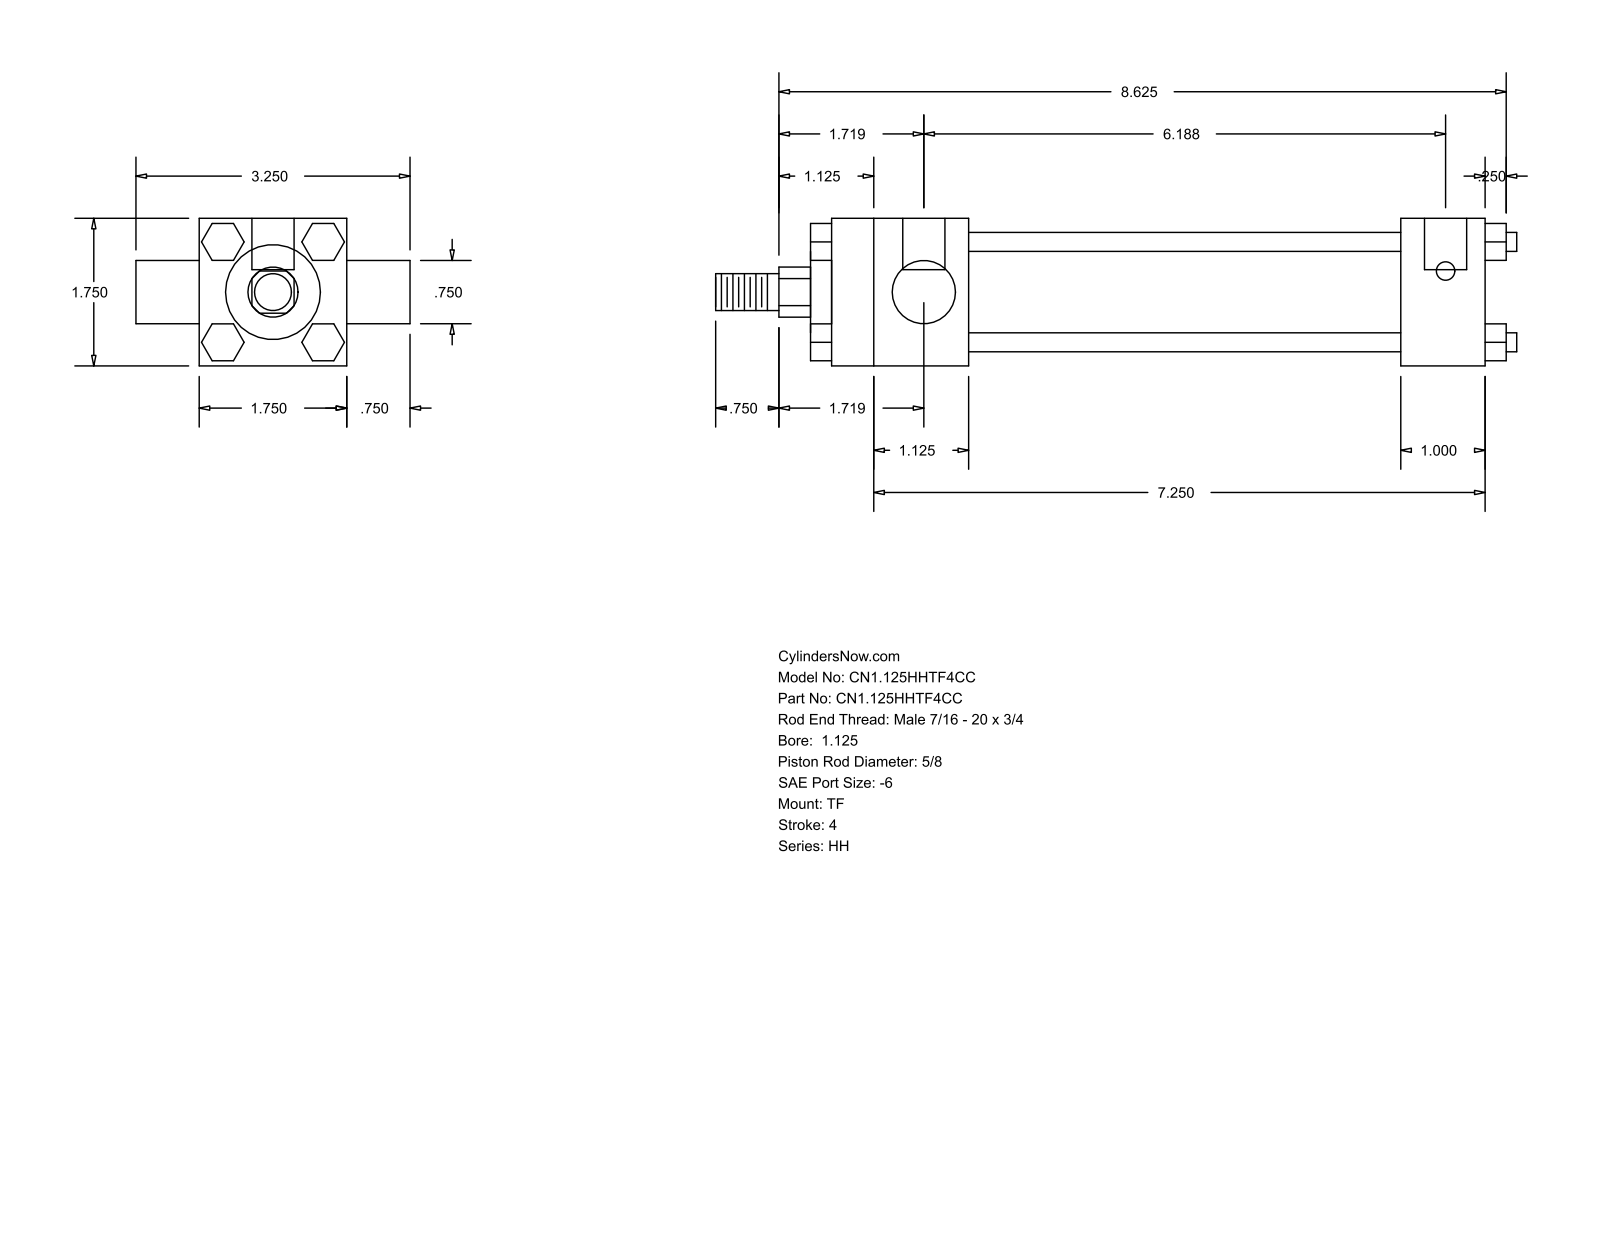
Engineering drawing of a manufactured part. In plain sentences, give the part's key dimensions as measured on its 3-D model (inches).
The part is named "HH_TF__0112_0.625". Its 3-D file was written by "GSSL Pune (CONFIG_CONTROL_DESIGN)". It is 0 solids with 120 faces: 92 planar, 28 cylindrical and 0 other. Overall it measures 9.5 by 3.25 by 1.75 inches. Round holes: 3 of diameter 0.219, 2 of diameter 0.5. Round bosses or shafts: 4 of diameter 0.225, 1 of diameter 1.375, 1 of diameter 1.125, 1 of diameter 0.75, 1 of diameter 0.625, 1 of diameter 0.437. Partial cylindrical surfaces (rounded edges, fillets, slot ends): 1 of radius 0.297. The main face-to-face distances are 1.75, 0.25, 8, 0.437, 1, 5.125, 6.125, 1.625, 6.75, 7.75. The hole center spacings are 0.125, 6.063, 6.187.
